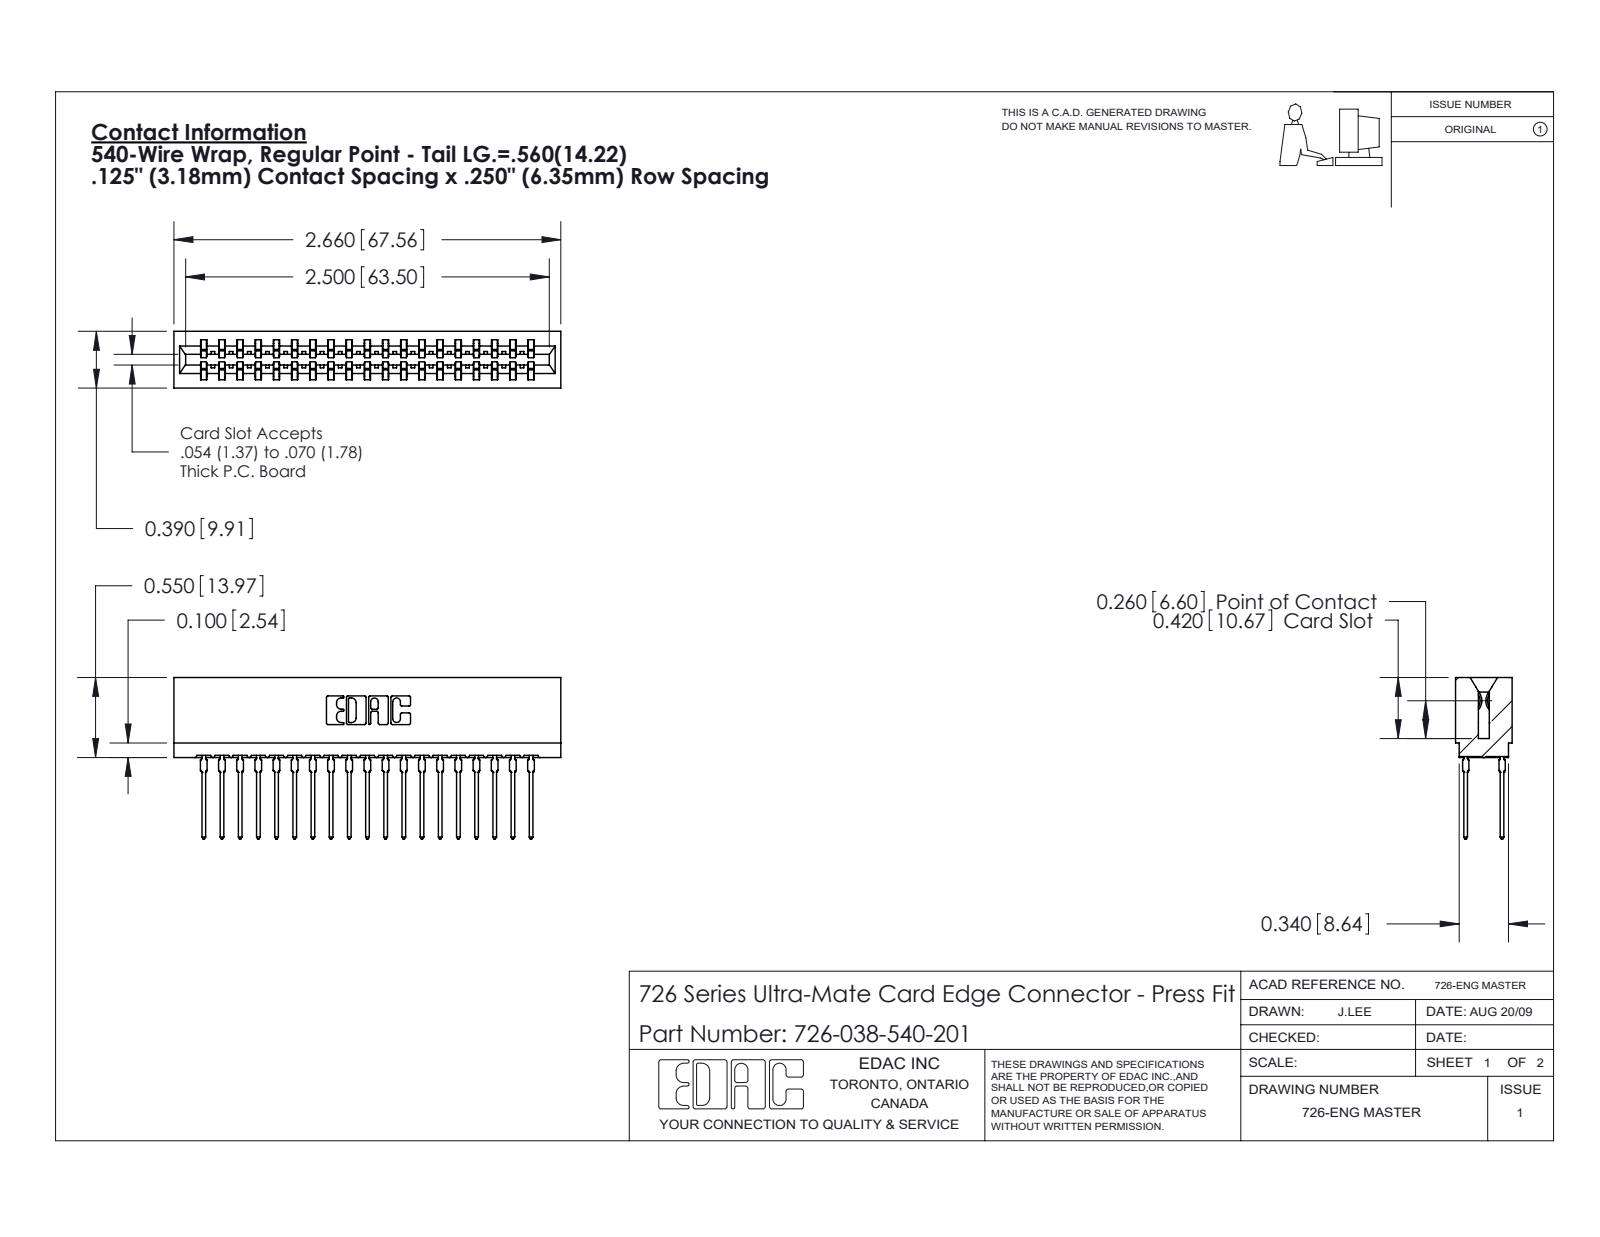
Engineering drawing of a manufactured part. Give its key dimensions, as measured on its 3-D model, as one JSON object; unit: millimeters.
{"part_name": "726 Part_.515 Slot Depth - 01; 726-038-540-201; 746-292-001_540", "step_written_by": "SolidWorks 2020 (CONFIG_CONTROL_DESIGN)", "units": "millimeters", "bodies": {"solids": 39, "faces": 3498, "planar": 1803, "cylindrical": 707, "other": 988}, "overall_size": [67.6, 28.2, 9.9], "volume_mm3": 6460, "surface_area_mm2": 10880, "partial_cylinders_radius": [[0.5, 76], [0.3, 22], [0.4, 20], [0.1, 8], [0.3, 8], [0.2, 6], [0.8, 6], [0.7, 3]], "face_to_face_distances": [1.4, 8.5, 6.4, 0.6, 7.8, 9.9, 12.7, 2.1, 7, 3.2]}
